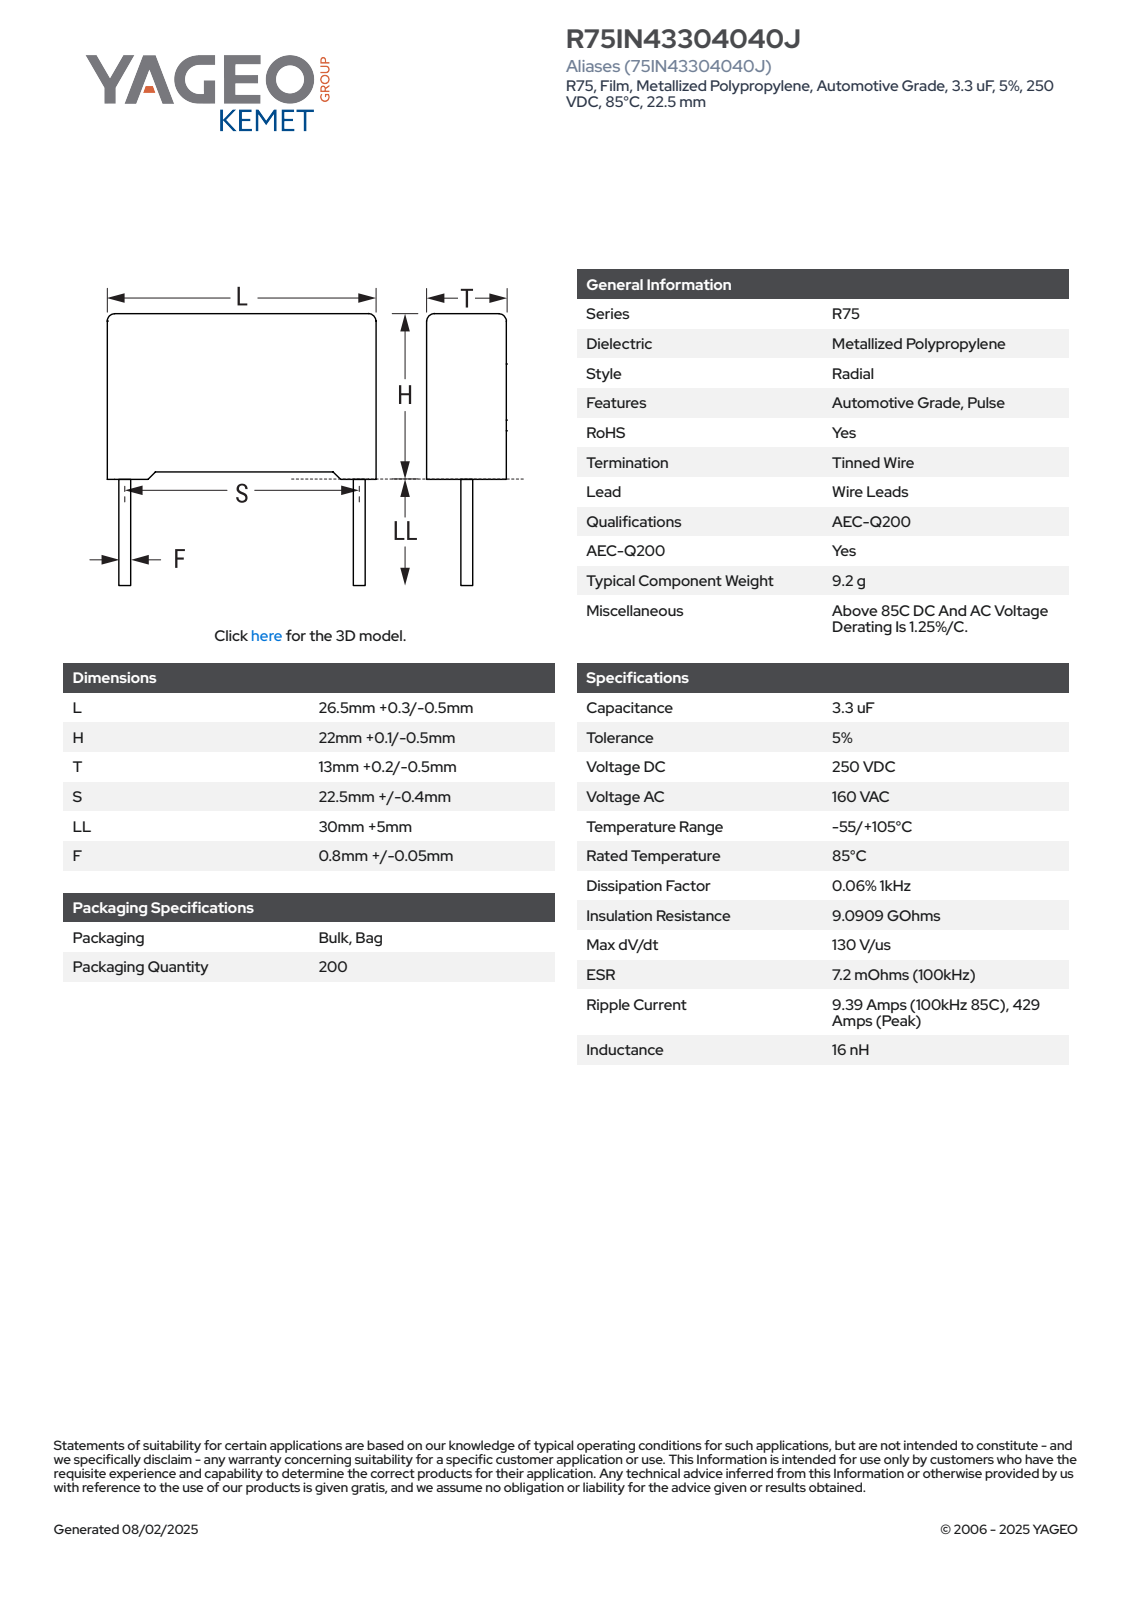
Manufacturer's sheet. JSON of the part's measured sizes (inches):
{"part_name": "CFR_RB2_26.5X22X13_L26.8H22.1T13.2S22.5LL35F0.85", "step_written_by": "SolidWorks 2021 (AUTOMOTIVE_DESIGN)", "units": "inches", "bodies": {"solids": 4, "faces": 85, "planar": 77, "cylindrical": 8, "other": 0}, "overall_size": [2.248, 1.055, 0.52], "volume_in3": 0.465, "surface_area_in2": 4.188, "round_bosses_or_shafts": [[0.033, 2]], "partial_cylinders_radius": [[0.02, 4]], "face_to_face_distances": [0.52, 1.055, 0.84, 0.841, 0.03, 0.03, 0.87, 0.035, 1.02, 0.52]}
